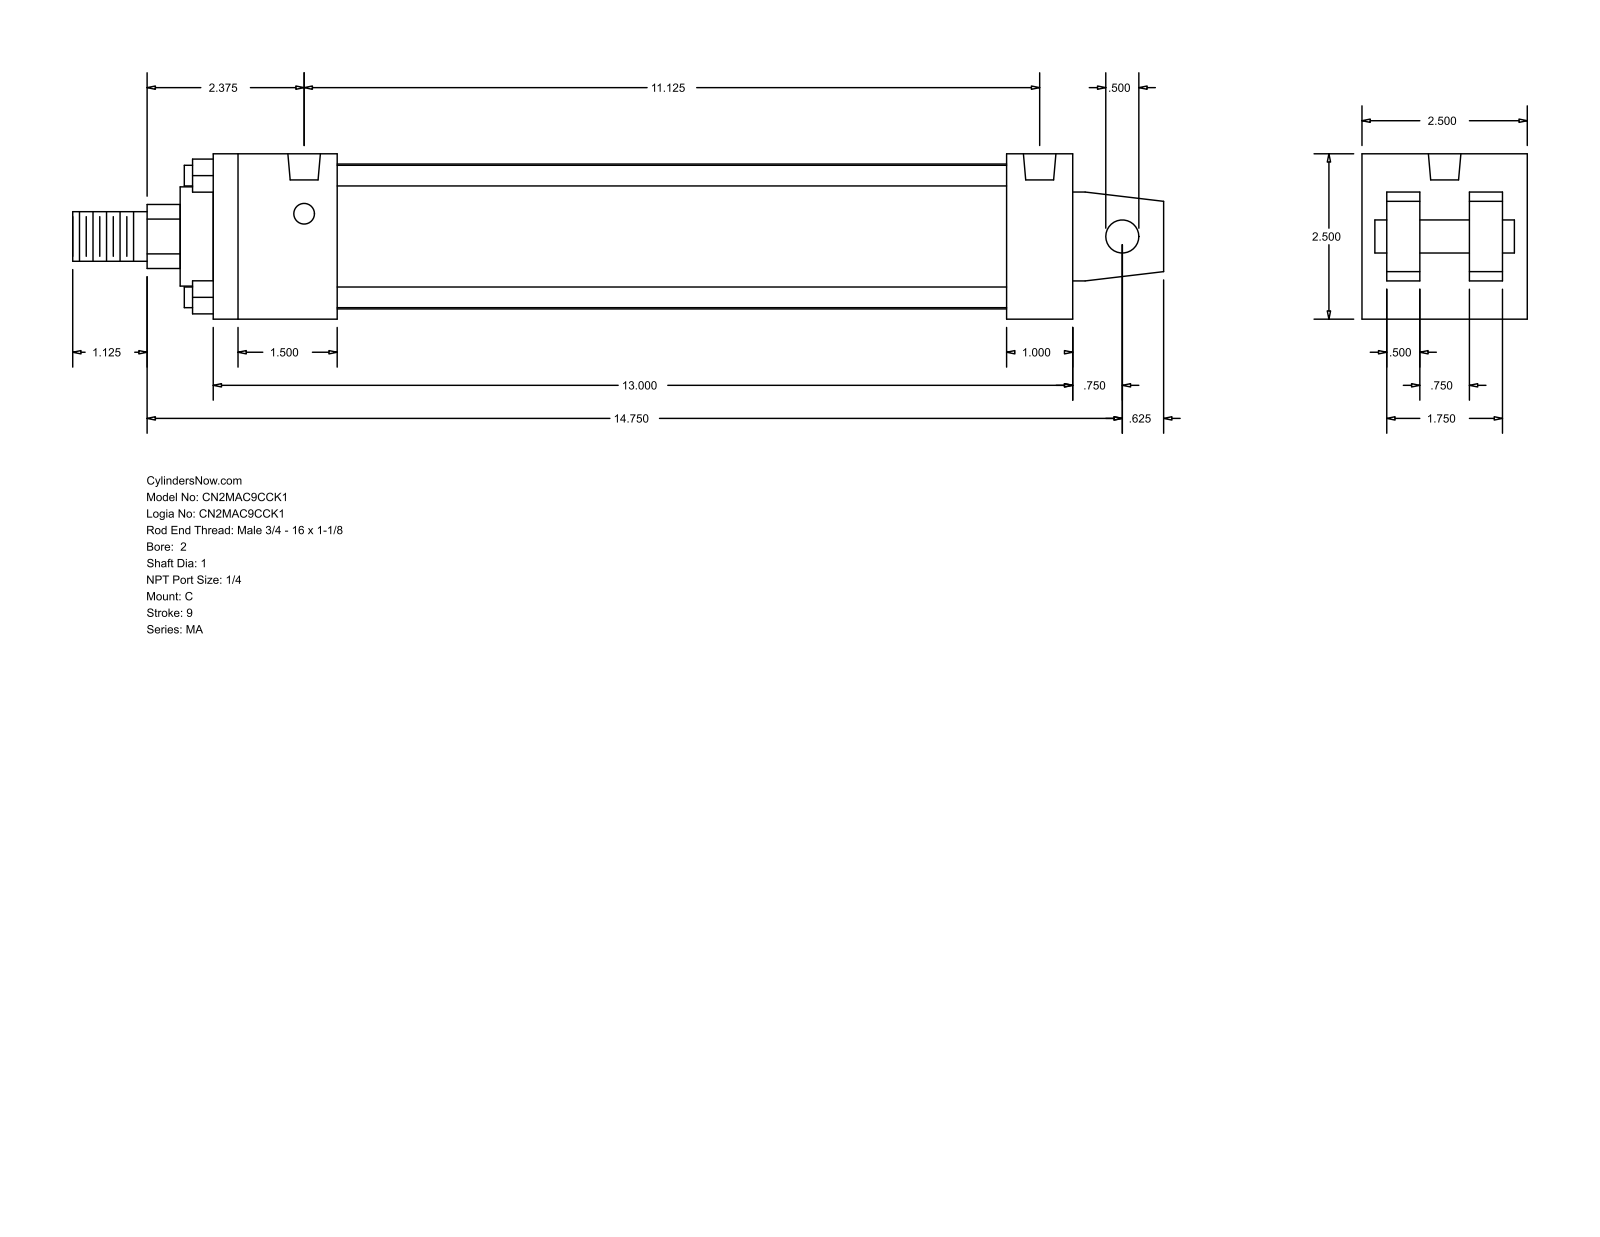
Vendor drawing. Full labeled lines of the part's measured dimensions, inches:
Part name (STEP PRODUCT): MA_C__0200_1
STEP written by: GSSL Pune (CONFIG_CONTROL_DESIGN)
Units: inches
Bodies: 0 solids, 103 faces (76 planar, 27 cylindrical, 0 other)
Overall size (bounding box): 16.5 × 2.5 × 2.5
Round holes (diameter × count): ⌀0.313 ×4, ⌀0.492 ×2
Round bosses / shafts (diameter × count): ⌀0.313 ×4, ⌀2.19 ×1, ⌀1.5 ×1, ⌀1 ×1, ⌀0.75 ×1, ⌀0.5 ×1
Partial cylindrical surfaces — rounded edges, fillets, slot ends (radius × count): R0.484 ×1
Main face-to-face distances: 2.5, 0.5, 13, 0.875, 1.625, 0.375, 2.125, 1.25, 1.875, 1
Hole centre spacings: 11.125
